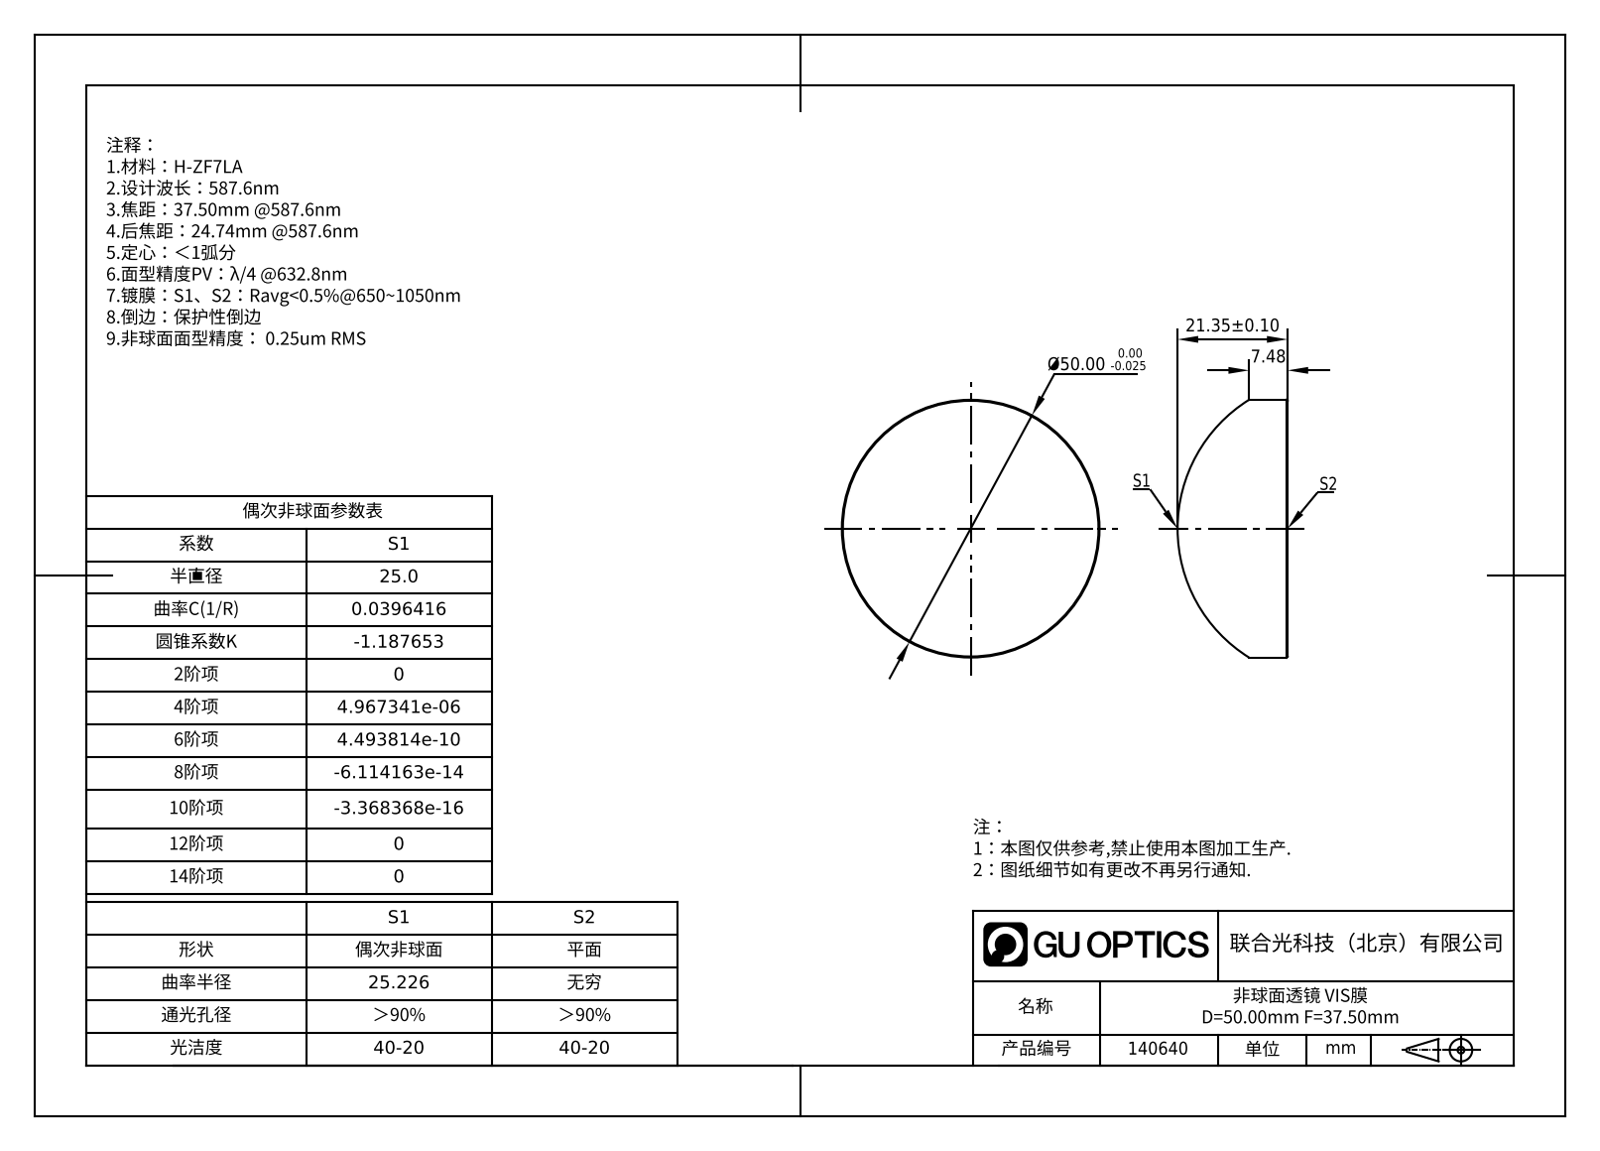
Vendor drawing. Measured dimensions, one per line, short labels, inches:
name: GLA11-050-37.5-H-VIS
written by: SolidWorks 2022 (AUTOMOTIVE_DESIGN)
unit: in
bodies: 1 solid, 7 faces (1 planar, 2 cylindrical, 4 other)
size: 1.969 × 1.969 × 0.84
volume: 1.811 in³; area: 8.813 in²
bosses: 1× ⌀1.969
